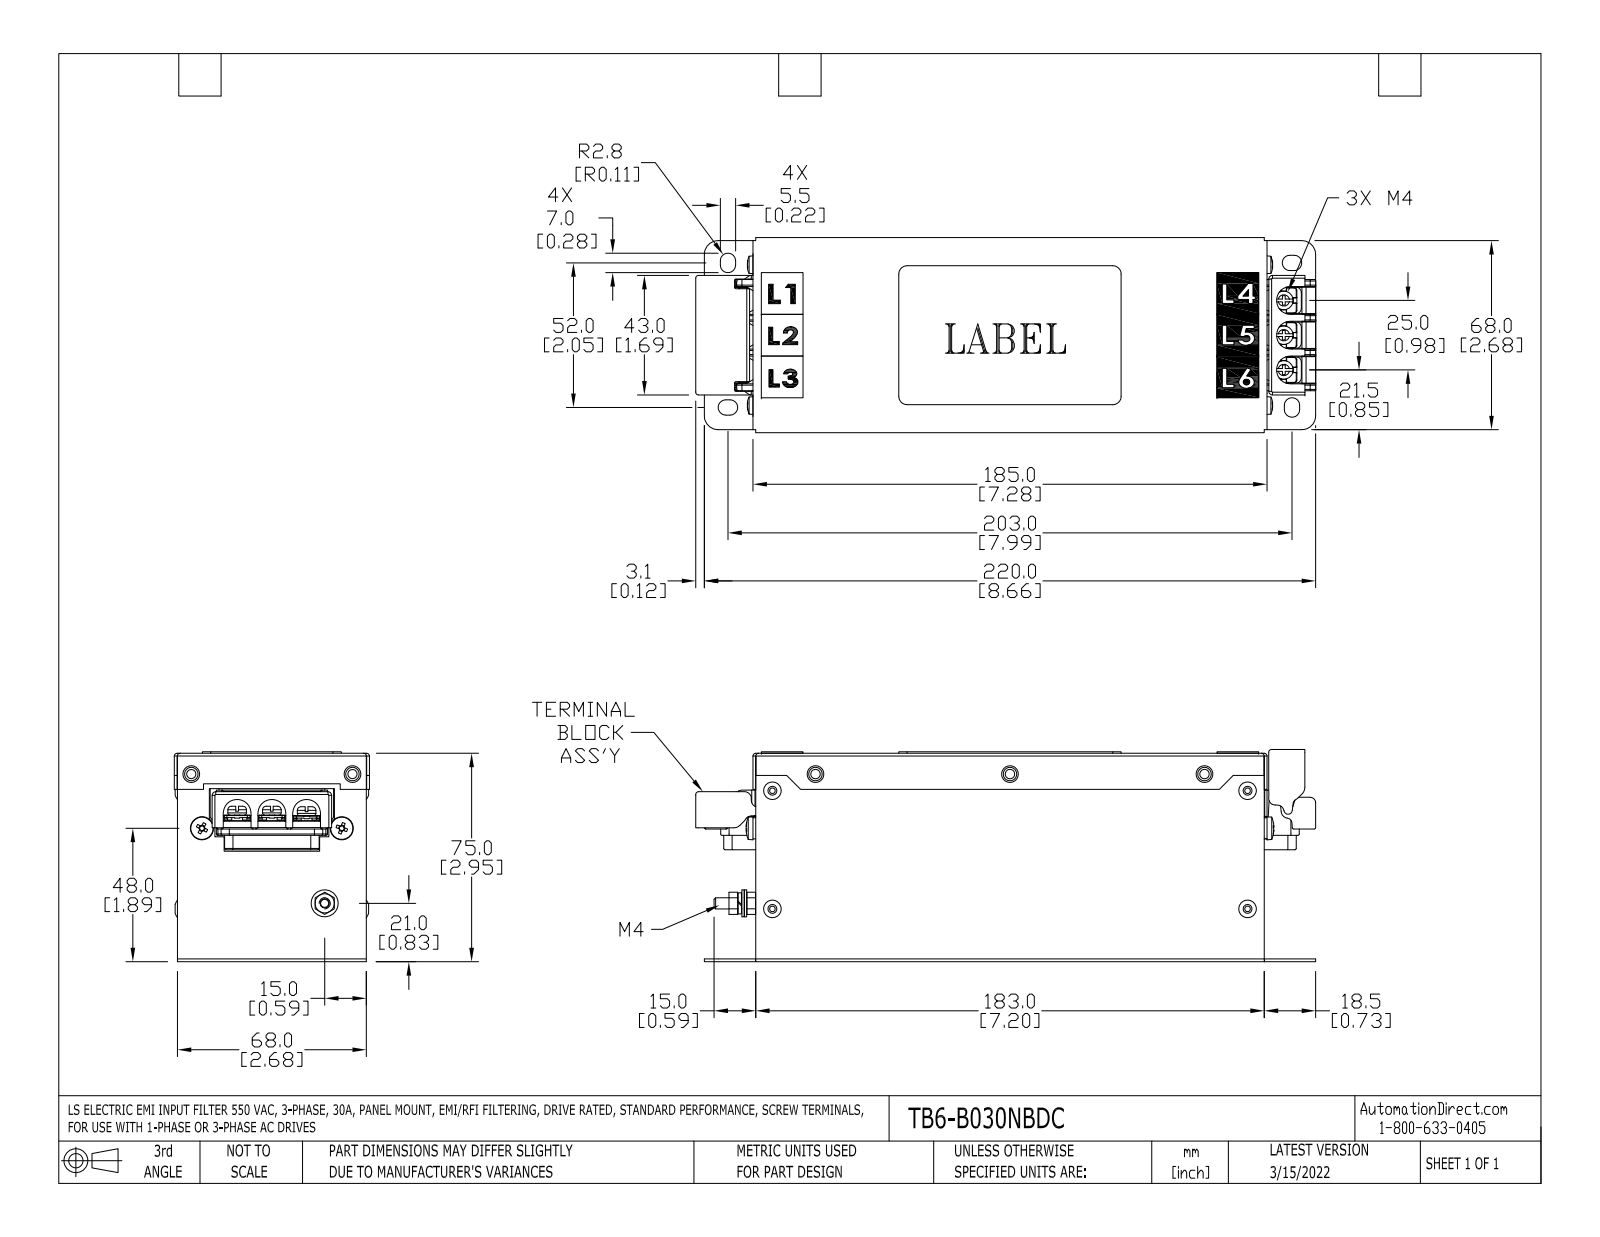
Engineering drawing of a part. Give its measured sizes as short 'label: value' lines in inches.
name: TB6-B020NBDC
written by: SolidWorks 2021 (AUTOMOTIVE_DESIGN)
unit: in
bodies: 47 solids, 1879 faces (876 planar, 526 cylindrical, 477 other)
size: 8.852 × 3.727 × 2.835
volume: 15.11 in³; area: 234.9 in²
holes: 13× ⌀0.079, 11× ⌀0.138, 10× ⌀0.13, 6× ⌀0.161, 1× ⌀0.154, 1× ⌀0.165, 1× ⌀0.205, 1× ⌀0.213
bosses: 13× ⌀0.138, 6× ⌀0.27, 6× ⌀0.254, 4× ⌀0.252, 2× ⌀0.054, 1× ⌀0.394, 1× ⌀0.262, 1× ⌀0.234
rounds: 116× R0.01, 13× R0.039, 12× R0.079, 8× R0.013, 8× R0.02, 8× R0.108, 7× R0.067, 3× R0.029
face distances: 0.047, 2.63, 2.953, 2.906, 2.441, 2.394, 0.512, 2.583, 2.677, 0.039
hole spacings: 0.394, 1.557, 6.717, 6.728, 1.807, 5.025, 6.811, 8.18
